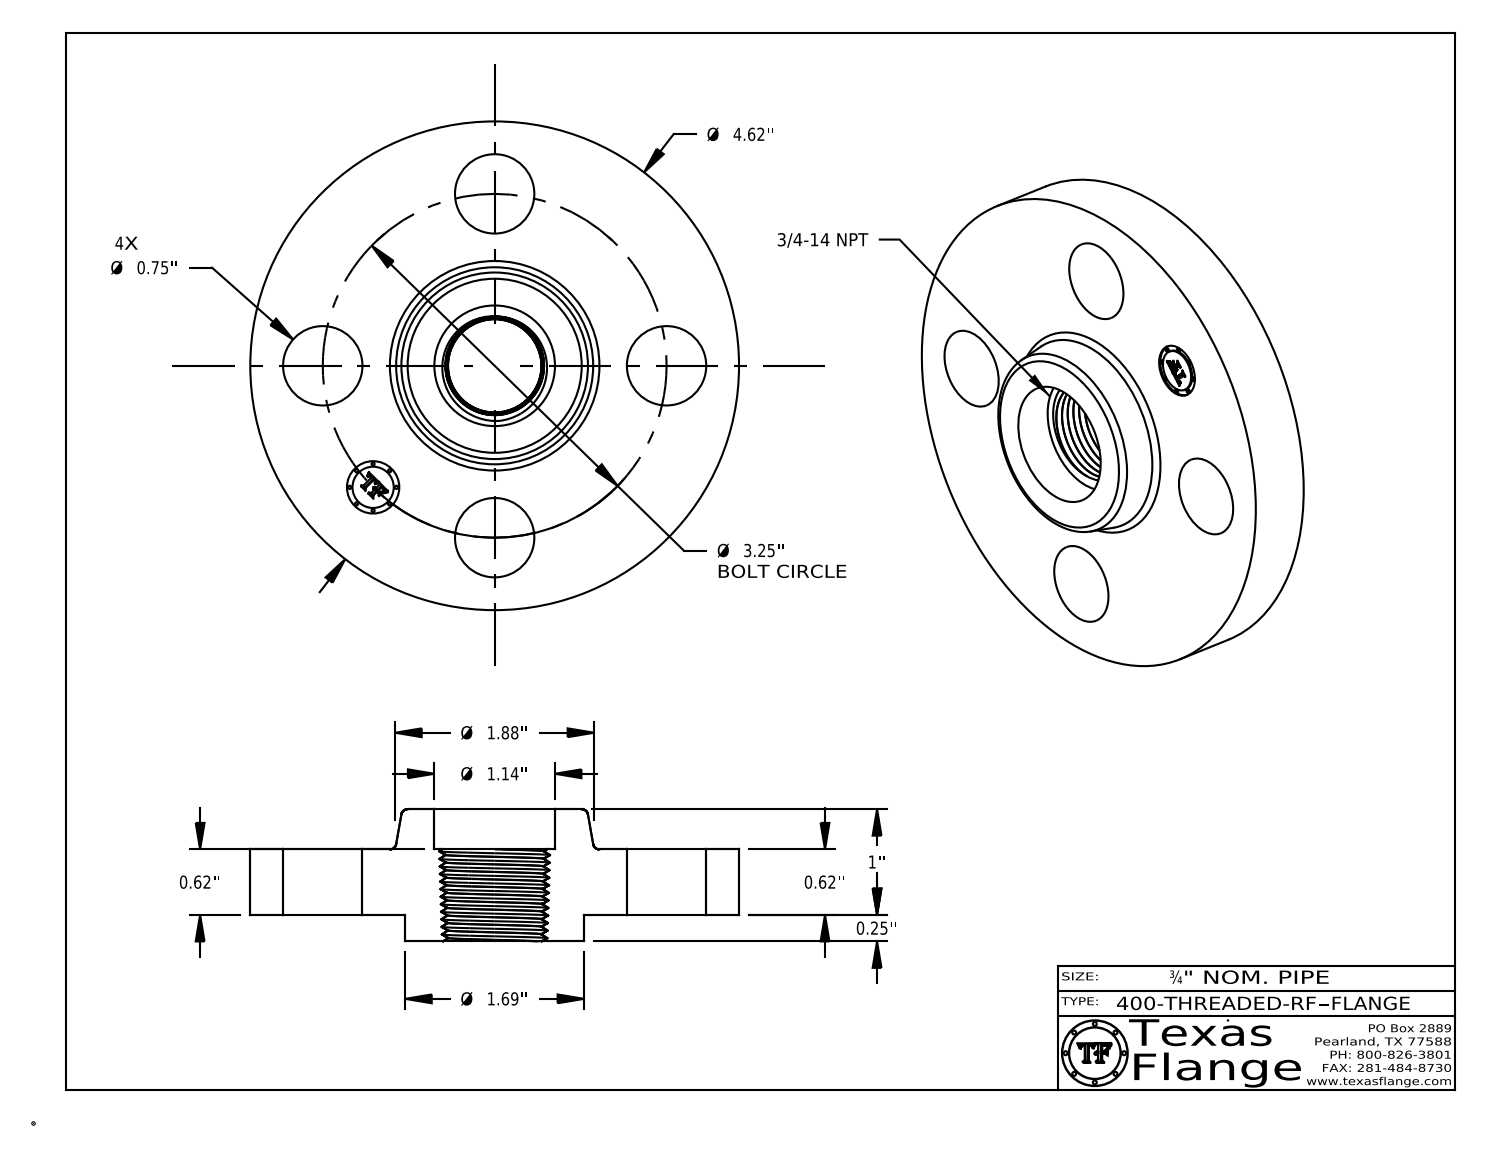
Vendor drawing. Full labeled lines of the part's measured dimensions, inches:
Part name (STEP PRODUCT): 400-THREADED-RF
STEP written by: CATIA V5 STEP AP214 (AUTOMOTIVE_DESIGN)
Units: inches
Bodies: 1 solid, 538 faces (370 planar, 34 cylindrical, 134 other)
Overall size (bounding box): 4.62 × 4.62 × 1.25
Volume: 9.819 in³ · Surface area: 52.7 in²
Round holes (diameter × count): ⌀0.75 ×4, ⌀0.495 ×1, ⌀1.14 ×1
Round bosses / shafts (diameter × count): ⌀0.03 ×8, ⌀4.62 ×1, ⌀1.69 ×1, ⌀0.39 ×1
Main face-to-face distances: 0.62, 0.25, 0.87, 1.25, 1, 0.38, 0.855, 0.605, 0.015, 0.395
Hole centre spacings: 1.625, 2.298, 1.244, 3.003, 3.25
